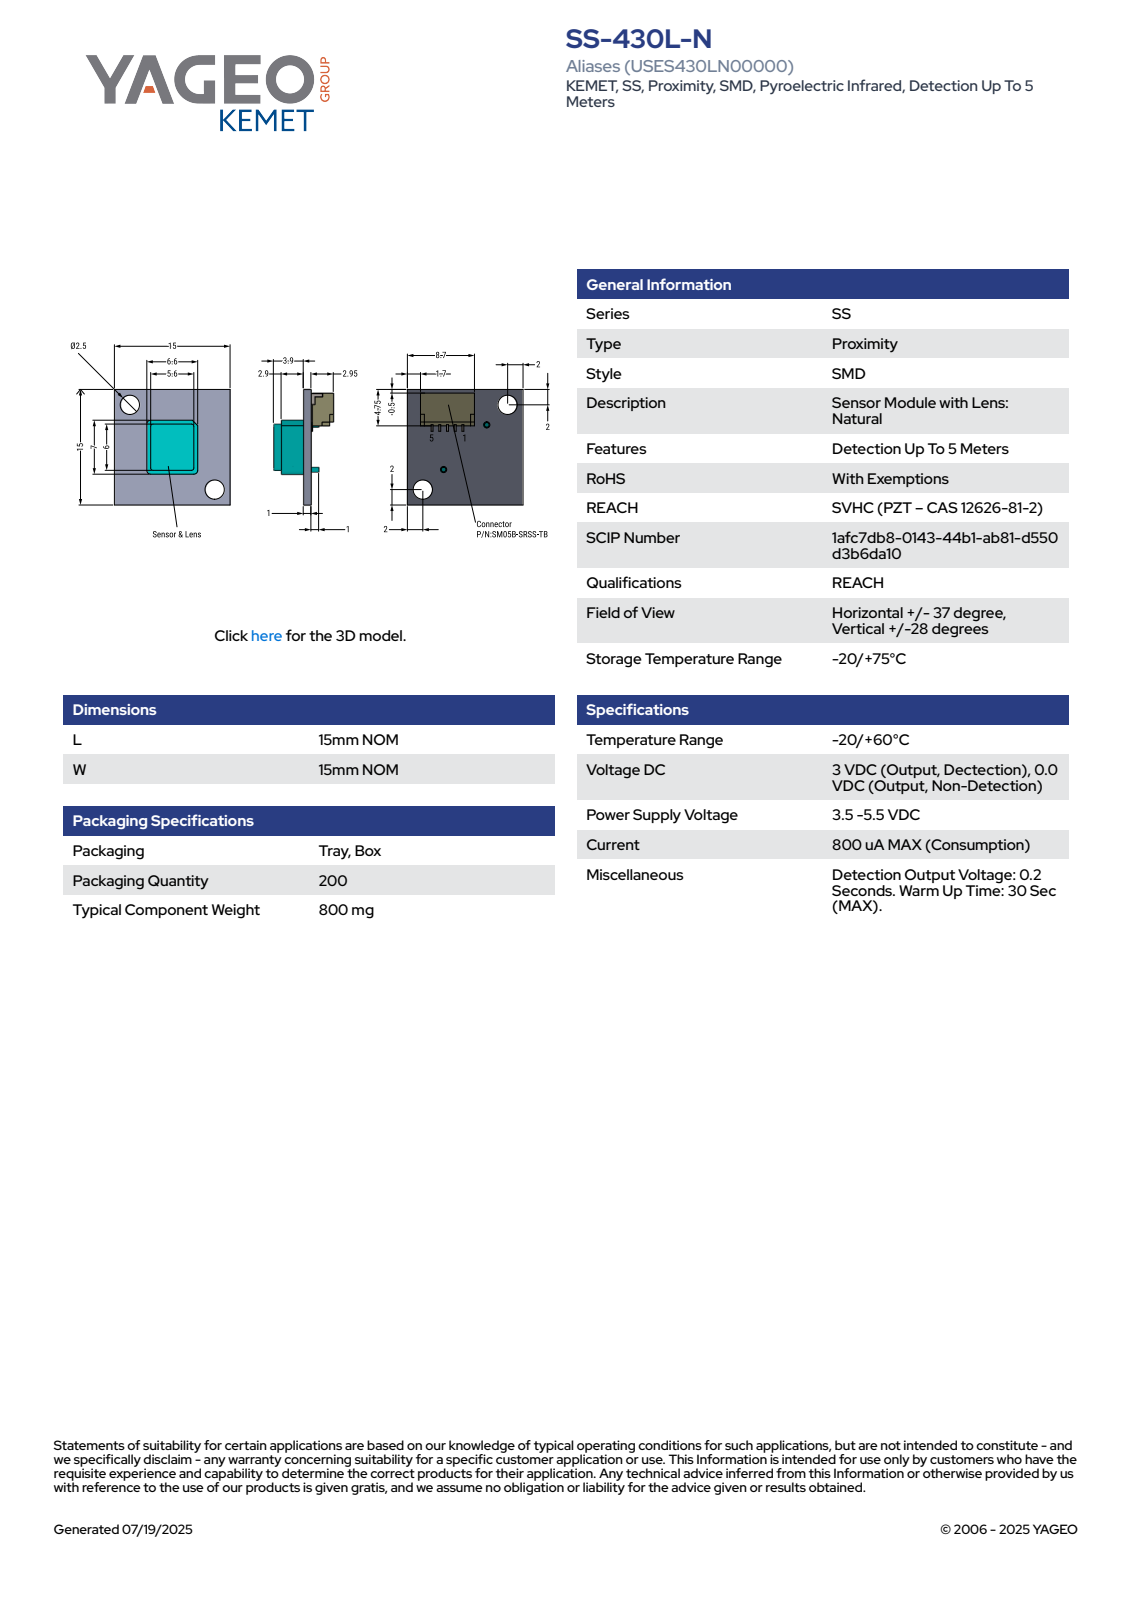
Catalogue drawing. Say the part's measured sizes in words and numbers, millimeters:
The part is named "SP_KSSL_L15W15". Its 3-D file was written by "SolidWorks 2014 (AUTOMOTIVE_DESIGN)". It is 1 solid with 93 faces: 78 planar, 15 cylindrical and 0 other. Overall it measures 15 by 15 by 7.86 millimeters. Its volume is 470 cubic millimeters and its surface area 674 square millimeters. Round holes: 2 of diameter 2.5. Round bosses or shafts: 2 of diameter 0.5. Partial cylindrical surfaces (rounded edges, fillets, slot ends): 4 of radius 0.25, 3 of radius 0.5. The main face-to-face distances are 1, 3.9, 4, 0.5, 4.9, 4.2, 10.8, 15, 11, 2.95. The hole center spacings are 15.56.
